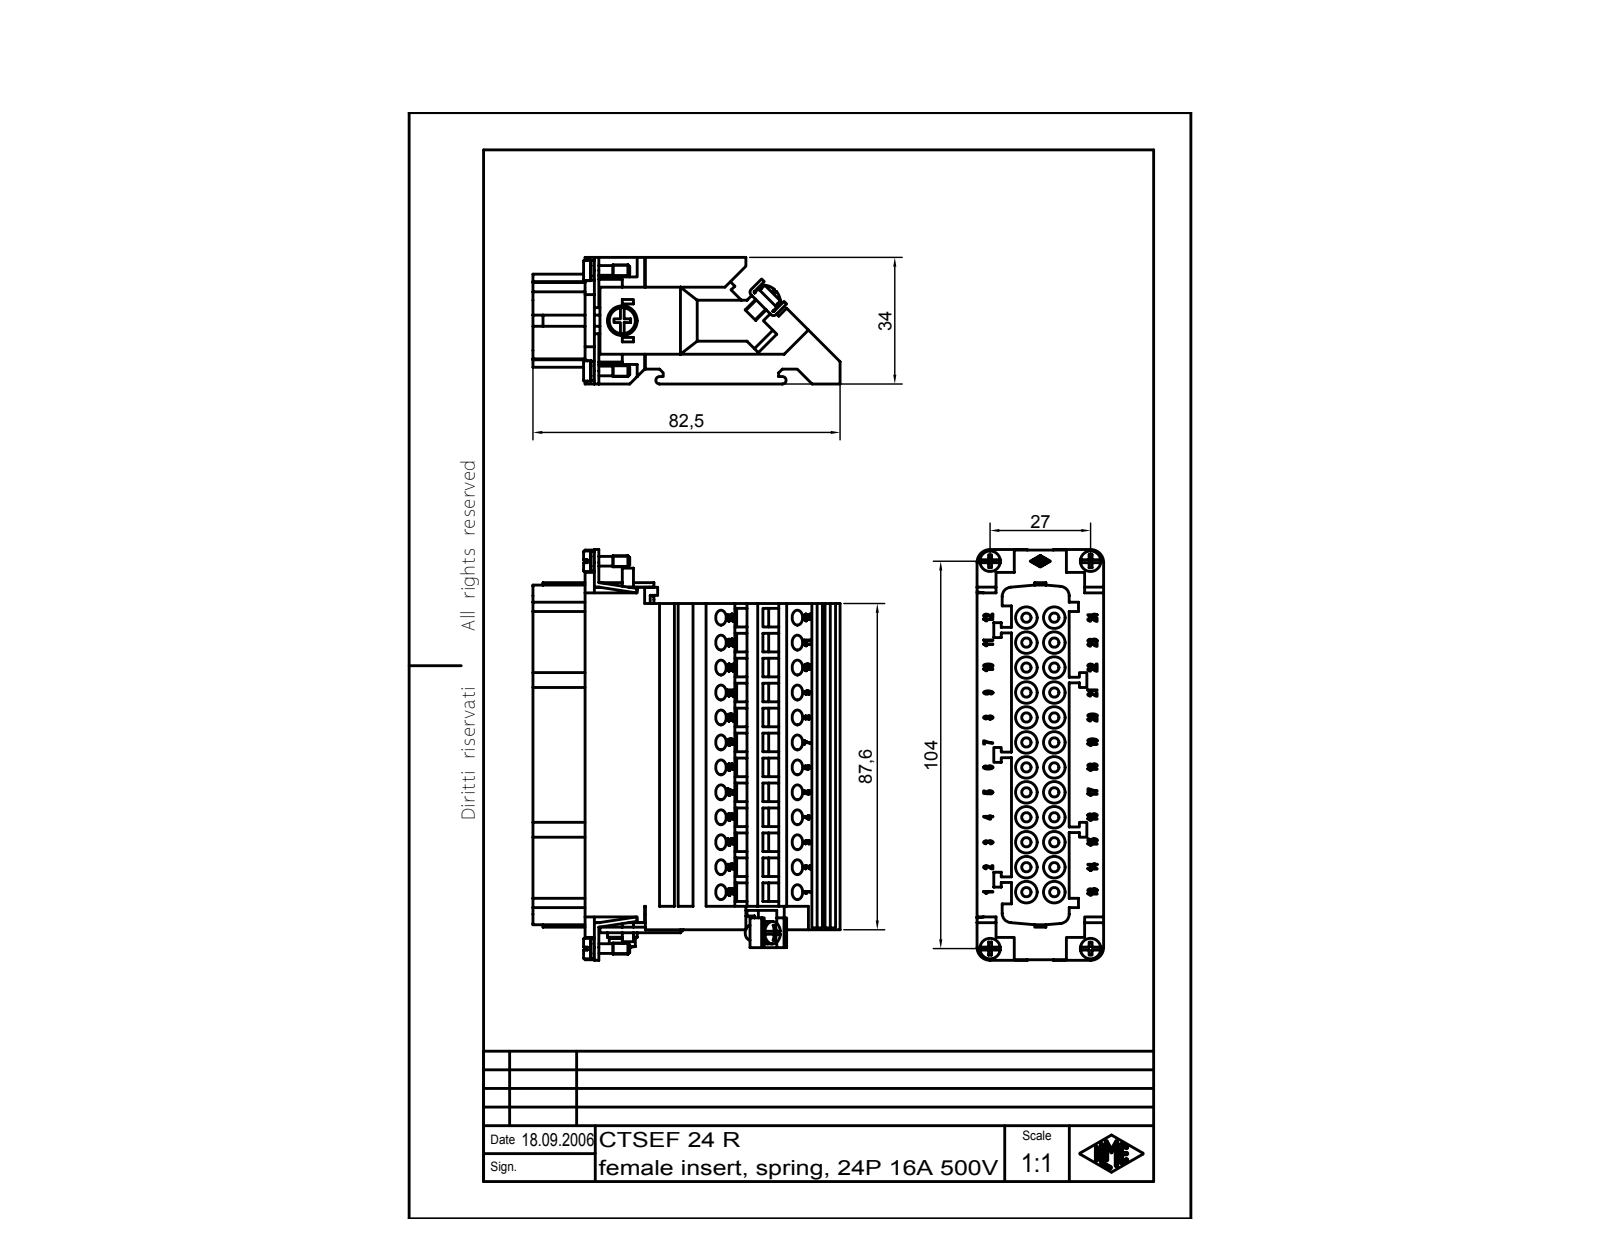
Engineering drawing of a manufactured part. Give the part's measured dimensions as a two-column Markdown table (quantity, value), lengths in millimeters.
| quantity | value |
| --- | --- |
| part name | CTSEF 24 R |
| STEP written by | Autodesk Inventor 7 (AUTOMOTIVE_DESIGN) |
| units | millimeters |
| bodies | 1 solid, 1979 faces (1014 planar, 106 cylindrical, 859 other) |
| overall size | 110.3 × 82.5 × 34 |
| volume | 168 154 mm³ |
| surface area | 41 245 mm² |
| round holes (diameter × count) | 4 × 24, 3.24 × 1 |
| round bosses / shafts (diameter × count) | 5.5 × 2, 5.3 × 2, 3 × 2, 2.6 × 2, 8 × 1, 7 × 1, 6 × 1, 4 × 1 |
| partial cylindrical surfaces (radius × count) | 0.1 × 14, 1 × 6, 2.5 × 4, 0.2 × 2, 3.5 × 2 |
| main face-to-face distances | 4, 34, 24.75, 9.25, 2, 5, 1.5, 8, 15.5, 30 |
| hole center spacings | 6.7, 24.31, 13.4, 26.94, 20.1, 30.82, 26.8, 35.56 |
